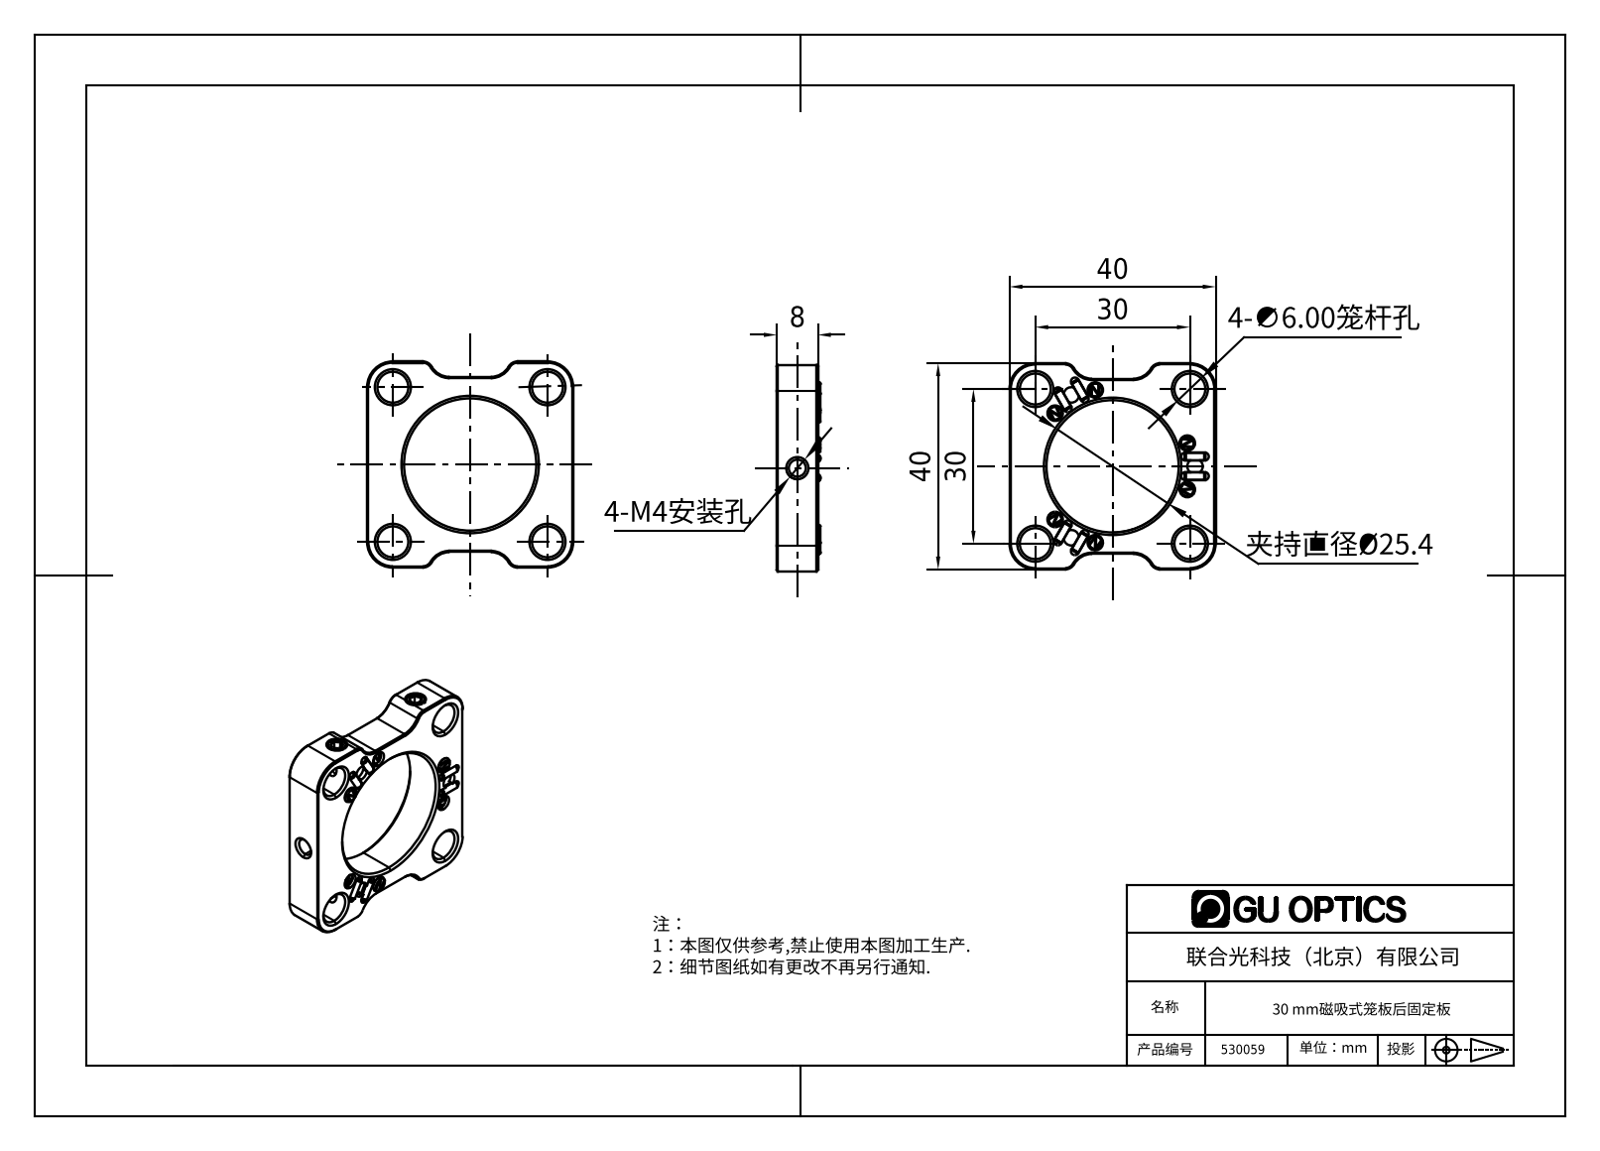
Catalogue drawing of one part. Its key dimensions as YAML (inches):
step_written_by: "SolidWorks 2018 (AUTOMOTIVE_DESIGN)"
units: inches
bodies: {solids: 0, faces: 411, planar: 172, cylindrical: 80, other: 159}
overall_size: [1.575, 1.575, 0.335]
round_holes:
  - {diameter: 0.236, count: 4}
  - {diameter: 0.118, count: 3}
  - {diameter: 0.13, count: 3}
  - {diameter: 1.01, count: 1}
round_bosses_or_shafts:
  - {diameter: 0.059, count: 6}
  - {diameter: 0.118, count: 3}
partial_cylinders:
  - {radius: 0.031, count: 12}
  - {radius: 0.079, count: 4}
  - {radius: 0.157, count: 4}
  - {radius: 0.197, count: 4}
  - {radius: 0.059, count: 3}
face_to_face_distances: [0.315, 1.575, 0.118, 1.457, 0.039, 0.276, 1.339, 1.322, 0.083, 0.016]
hole_center_spacings: [0.835, 1.181, 1.035, 0.598, 1.67, 0.239, 0.414, 0.459]
